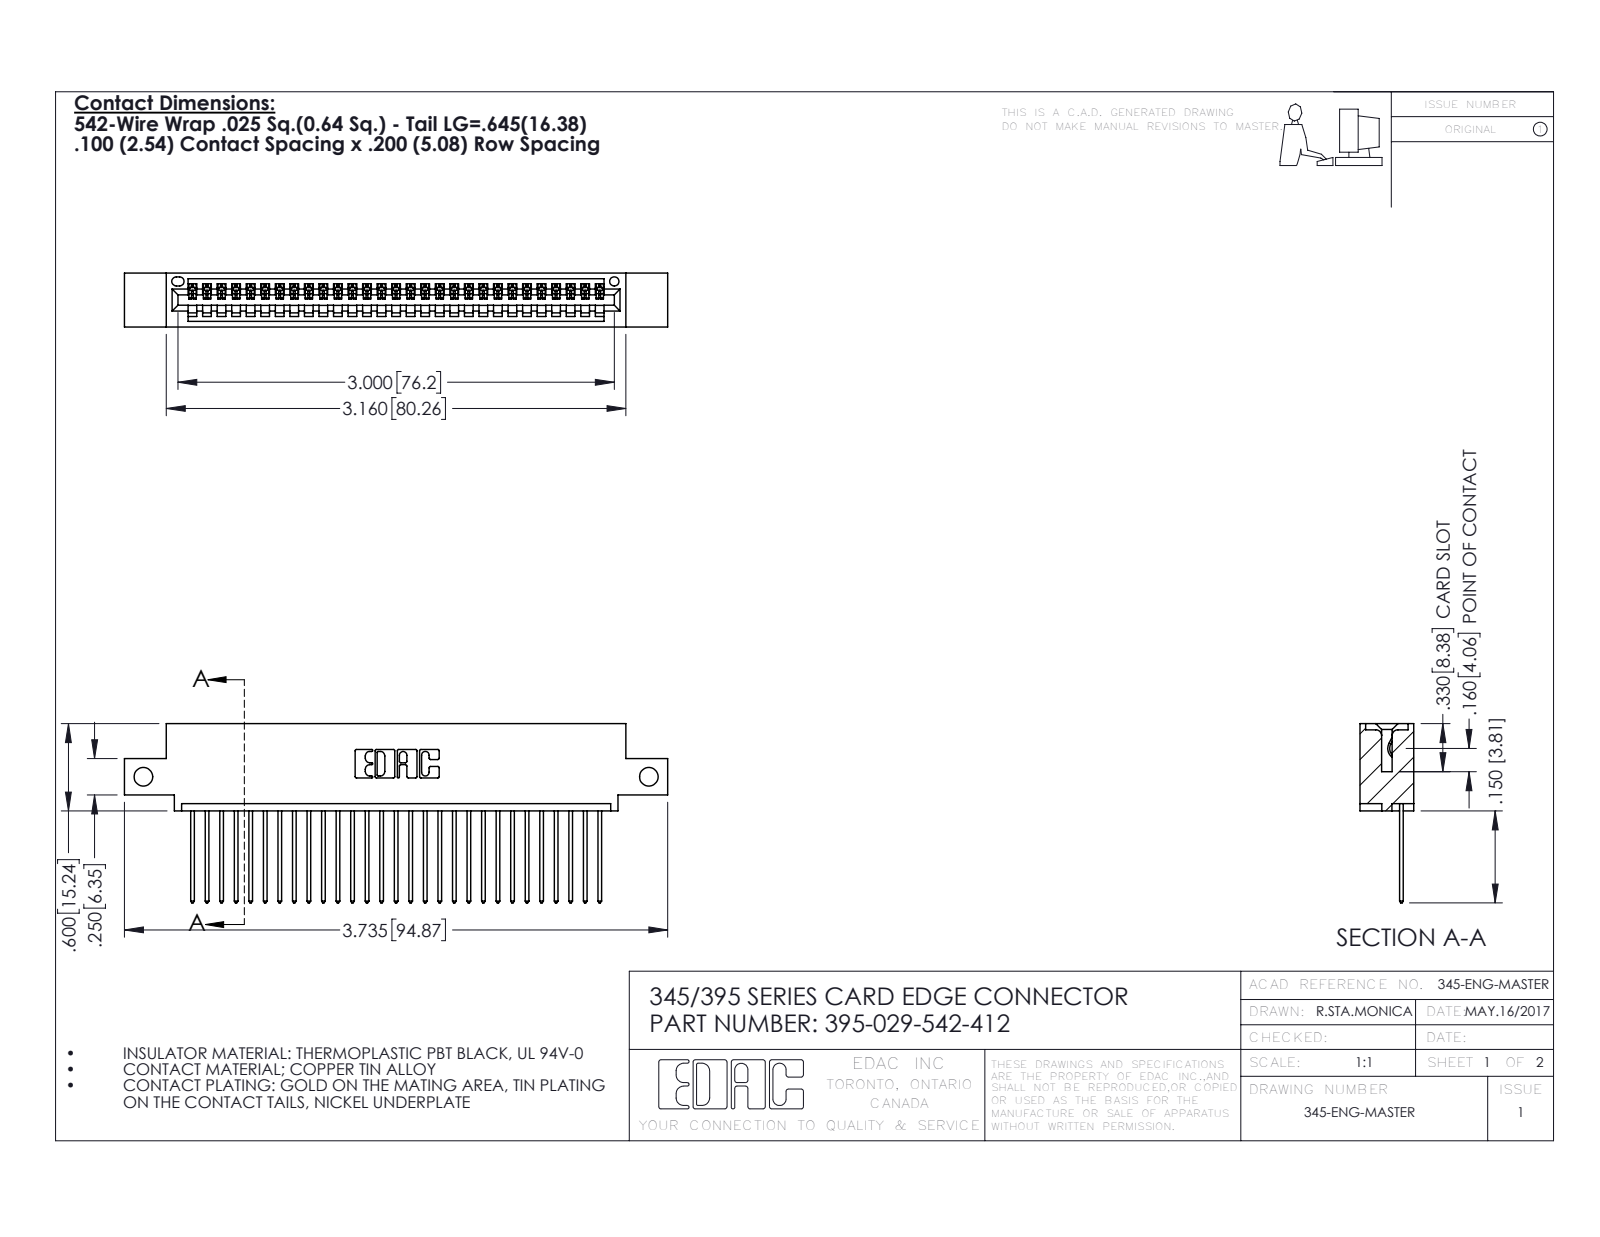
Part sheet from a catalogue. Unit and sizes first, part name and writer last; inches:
Units: inches
Overall size (bounding box): 3.735 × 1.232 × 0.37
Round holes (diameter × count): ⌀0.128 ×2, ⌀0.064 ×1
Partial cylindrical surfaces — rounded edges, fillets, slot ends (radius × count): R0.006 ×58, R0.01 ×58, R0.01 ×22, R0.007 ×6, R0.031 ×6, R0.026 ×3, R0.031 ×2, R0.04 ×2
Main face-to-face distances: 0.298, 0.072, 0.37, 0.098, 0.272, 0.025, 0.2, 0.225, 0.149, 0.072
Hole centre spacings: 3.475
Volume: 0.538 in³ · Surface area: 18.41 in²
Bodies: 30 solids, 1812 faces (1244 planar, 568 cylindrical, 0 other)
Part name (STEP PRODUCT): 345-292-001_345-293-142; 345 Part_0.110 Offset - Side Mount; 395-029-542-412
STEP written by: SolidWorks 2016 (CONFIG_CONTROL_DESIGN)
